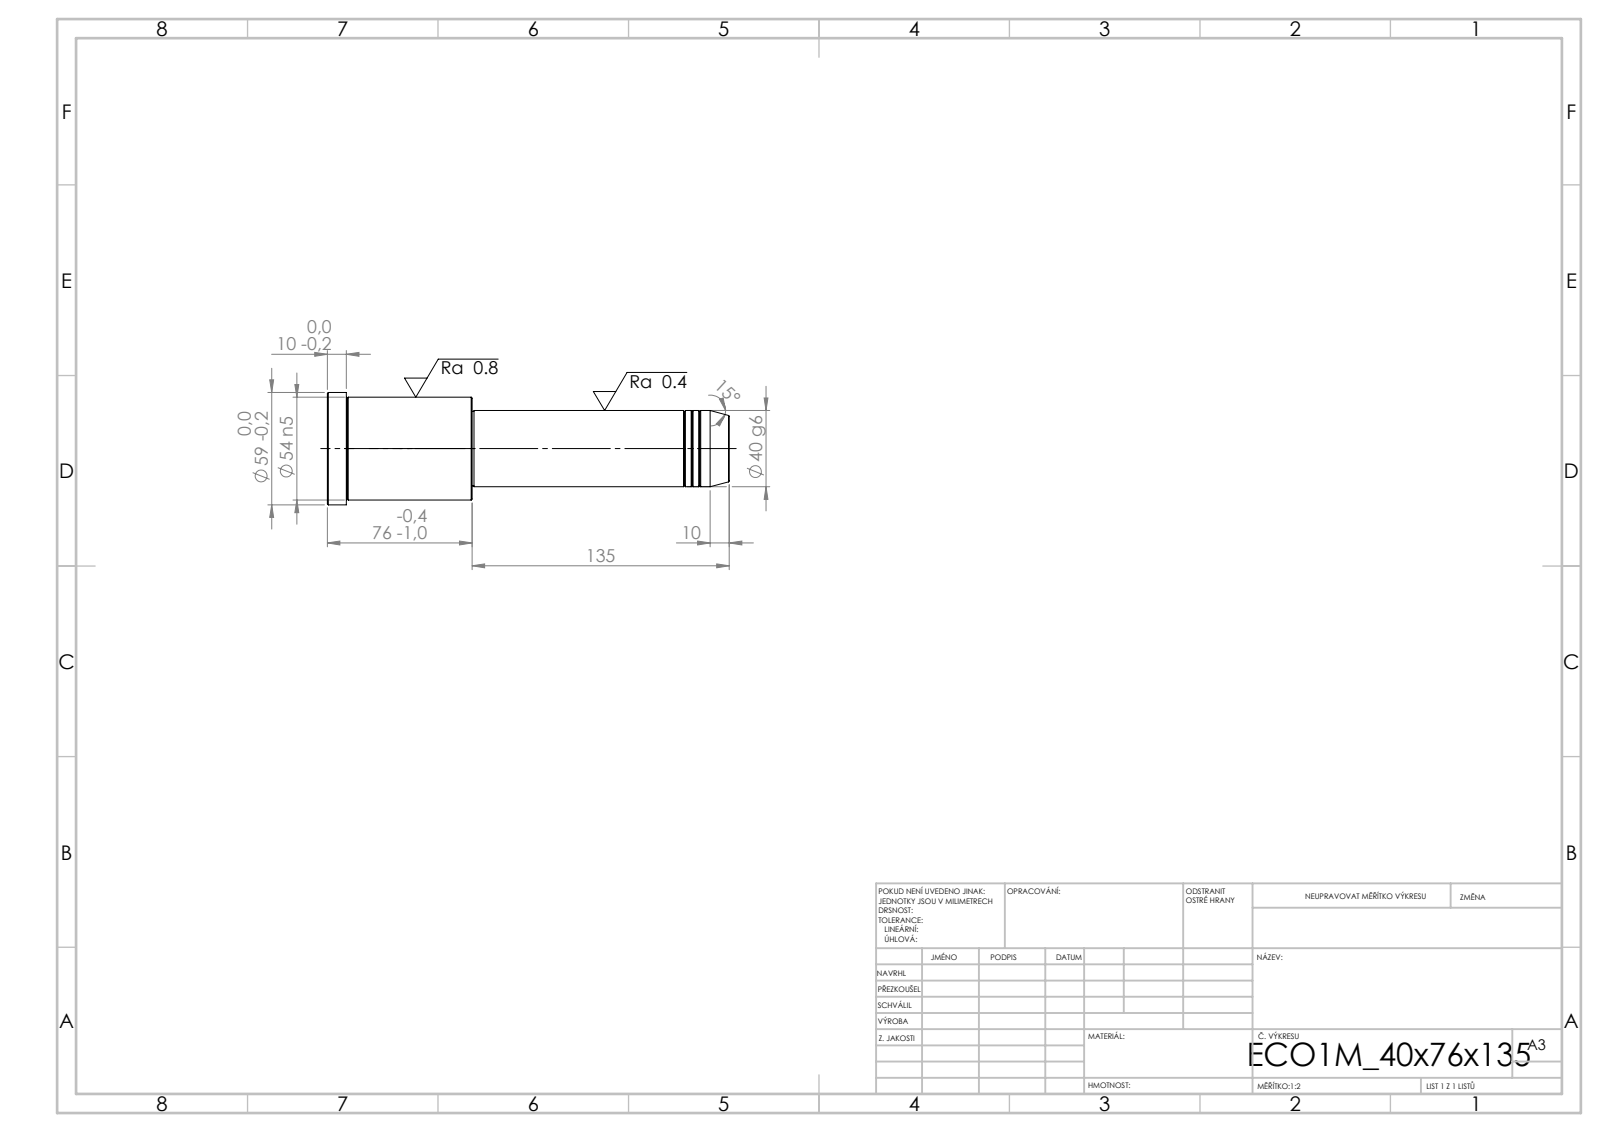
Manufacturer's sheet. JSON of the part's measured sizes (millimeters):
{"step_written_by": "SolidWorks 2019 (CONFIG_CONTROL_DESIGN)", "units": "millimeters", "bodies": {"solids": 1, "faces": 43, "planar": 5, "cylindrical": 14, "other": 24}, "overall_size": [211, 59, 59], "volume_mm3": 346210, "surface_area_mm2": 35429, "round_bosses_or_shafts": [[59, 1], [54, 1], [40, 1], [39, 1]], "face_to_face_distances": [76, 135, 211, 201, 66, 10, 134, 1, 67, 77]}
